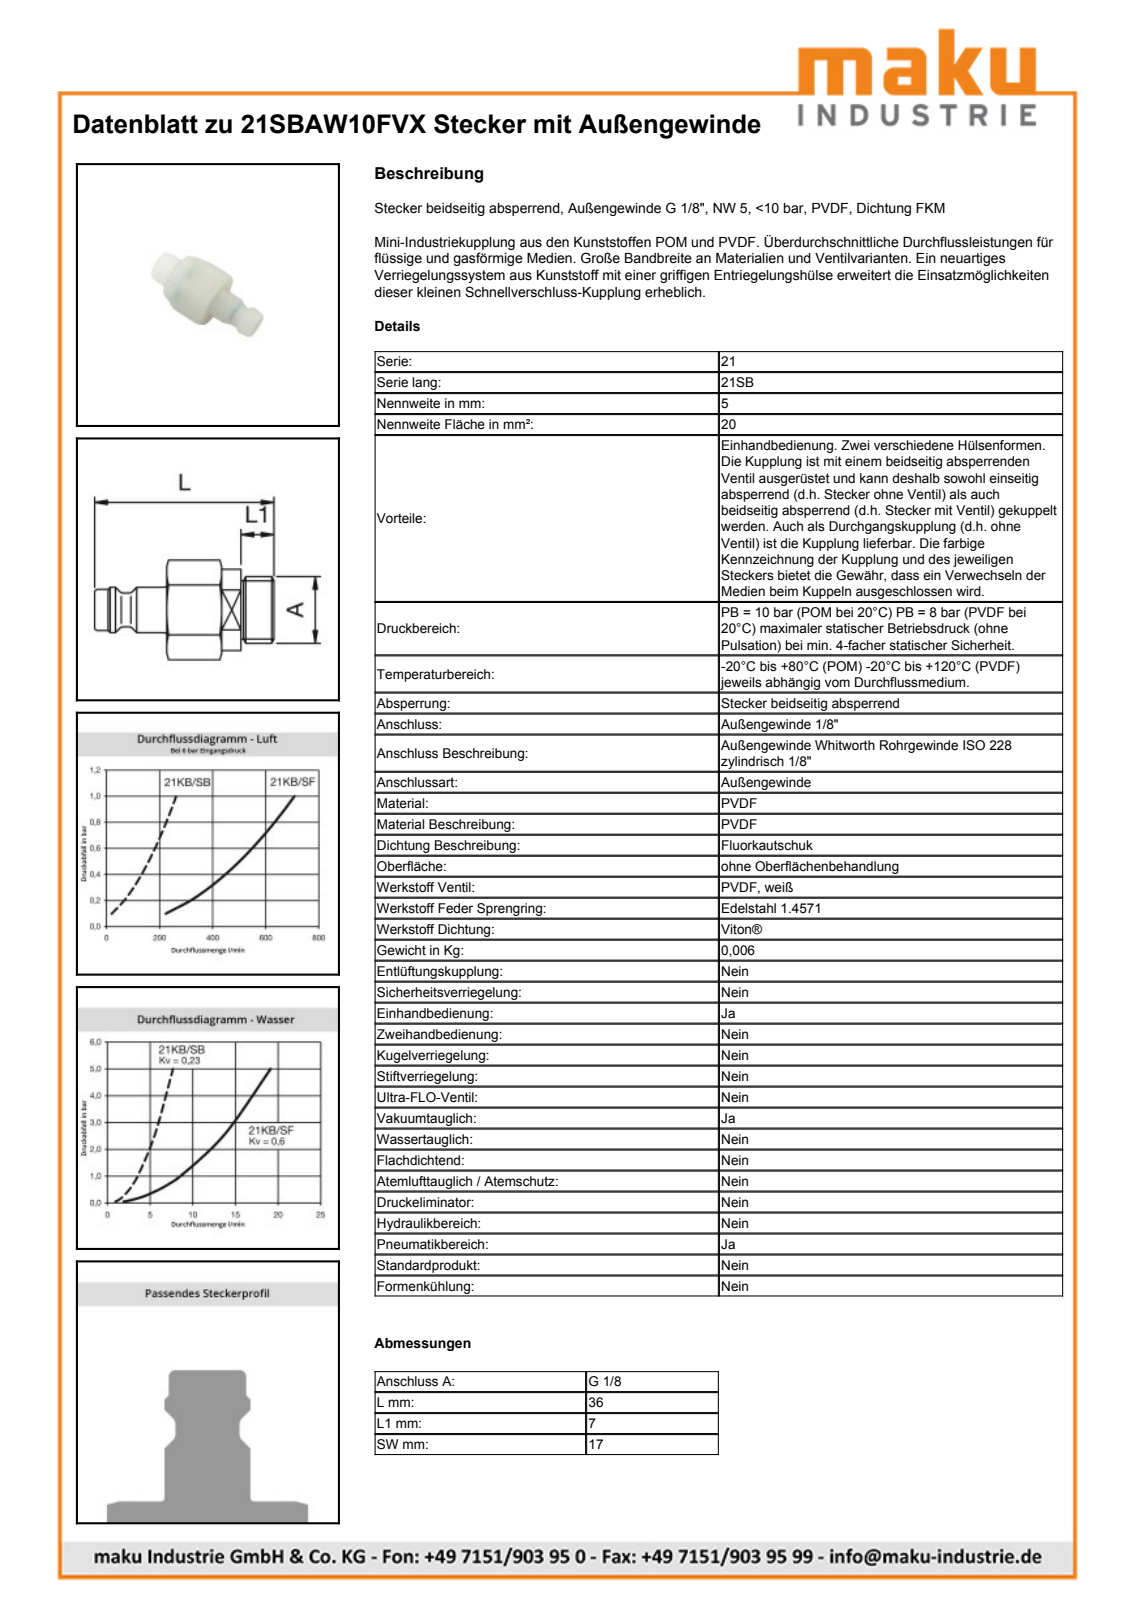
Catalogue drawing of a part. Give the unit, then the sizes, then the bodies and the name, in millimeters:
Units: millimetres
Overall size (bounding box): 35.8 × 19.63 × 17
Round holes (diameter × count): ⌀11.45 ×1, ⌀13.3 ×1
Round bosses / shafts (diameter × count): ⌀10.5 ×1, ⌀9.73 ×1, ⌀9.08 ×1, ⌀9 ×1, ⌀8.85 ×1, ⌀8.57 ×1, ⌀8.15 ×1, ⌀6.65 ×1
Partial cylindrical surfaces — rounded edges, fillets, slot ends (radius × count): R8 ×1
Main face-to-face distances: 17, 14.65, 10.85, 3.8, 21.65, 10.8, 7, 2.85, 8, 11.8
Volume: 4 572 mm³ · Surface area: 2 330 mm²
Bodies: 1 solid, 50 faces (16 planar, 14 cylindrical, 20 other)
Part name (STEP PRODUCT): D108730
STEP written by: Autodesk Inventor 2013 (AUTOMOTIVE_DESIGN)
